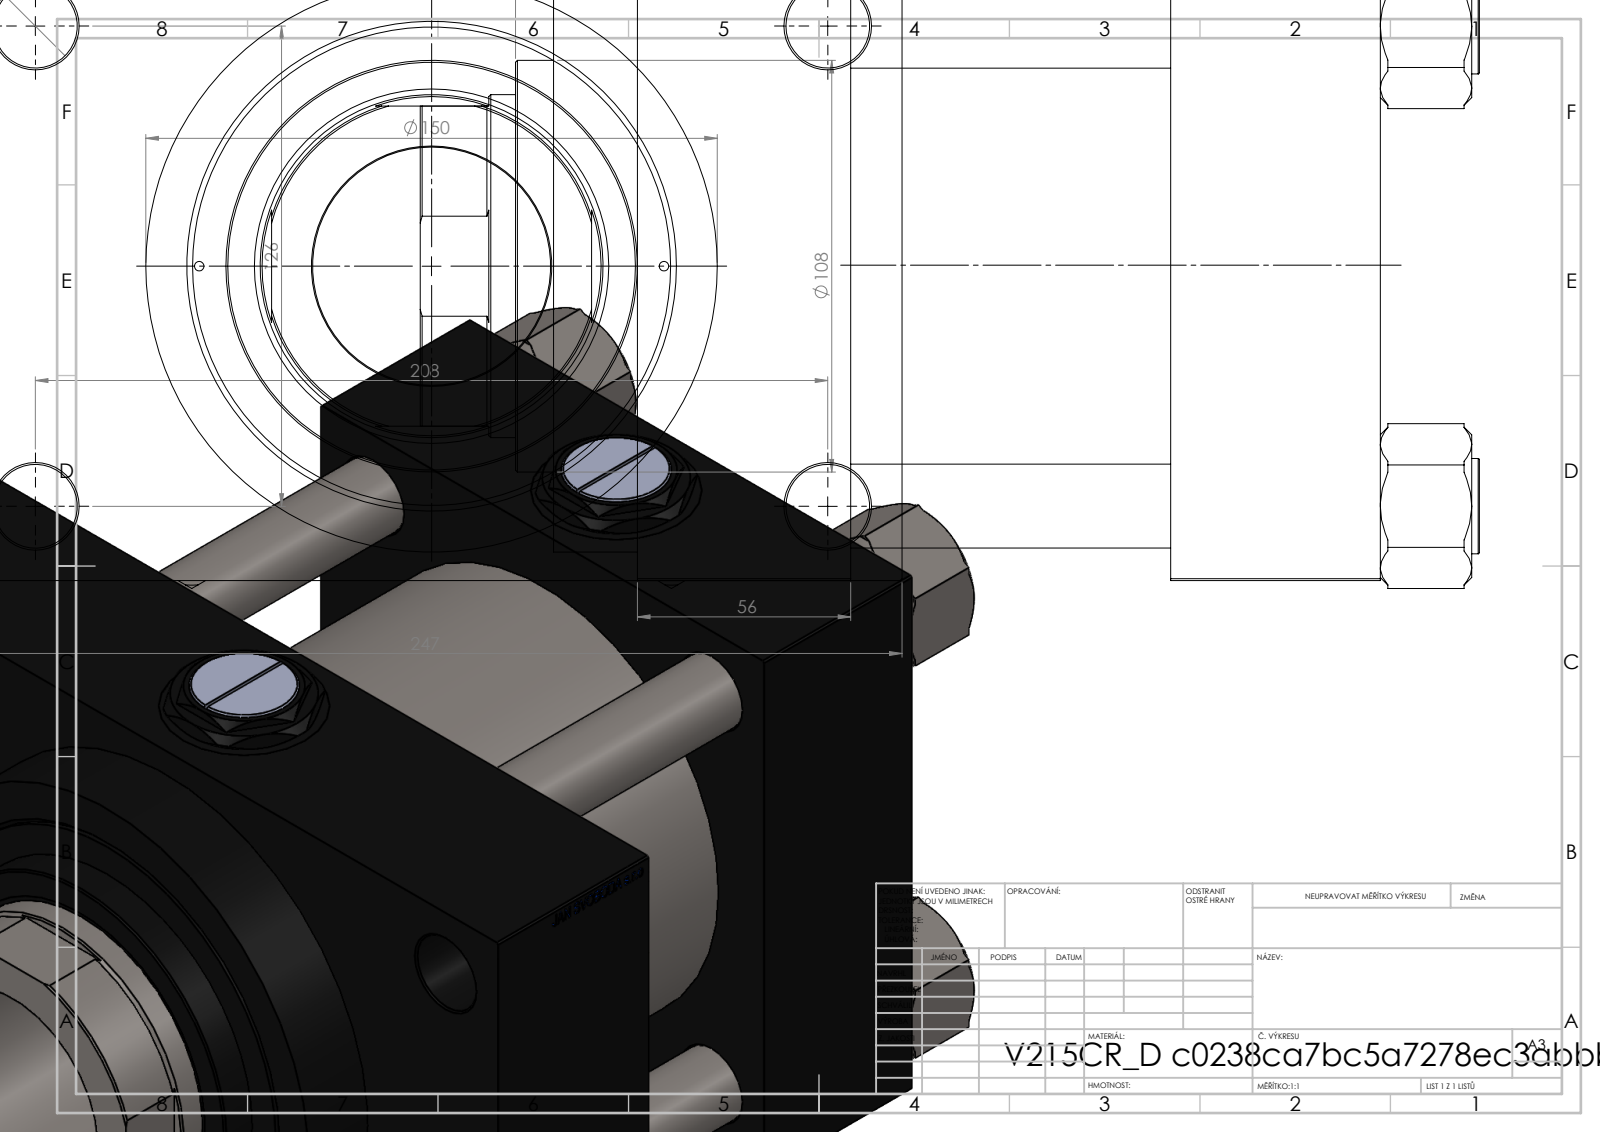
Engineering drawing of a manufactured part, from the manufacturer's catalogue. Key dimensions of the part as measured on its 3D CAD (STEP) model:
Part name (STEP PRODUCT): NUT_M5_D; V215CR_D_Body; Zatka_pro_OIL_PORT; V215CR_D_TYCINKA (+2 more)
STEP written by: SolidWorks 2019 (CONFIG_CONTROL_DESIGN)
Units: millimetres
Bodies: 13 solids, 1260 faces (595 planar, 103 cylindrical, 562 other)
Overall size (bounding box): 278 × 247 × 174.07
Volume: 5 164 000 mm³ · Surface area: 586 395 mm²
Round holes (diameter × count): ⌀22 ×8, ⌀32.24 ×4, ⌀45 ×4, ⌀7 ×3, ⌀2.5 ×2, ⌀62.5 ×1, ⌀90 ×1, ⌀93 ×1, ⌀96 ×1, ⌀125 ×1, ⌀125.5 ×1
Round bosses / shafts (diameter × count): ⌀25 ×4, ⌀150 ×1, ⌀131 ×1, ⌀108 ×1
Partial cylindrical surfaces — rounded edges, fillets, slot ends (radius × count): R44 ×1
Main face-to-face distances: 84, 165, 55, 139, 195, 140, 56, 41, 206, 173.74
Hole centre spacings: 41.05, 62.98, 76.28, 89.02, 121.59, 125.9, 132.47, 139.02
